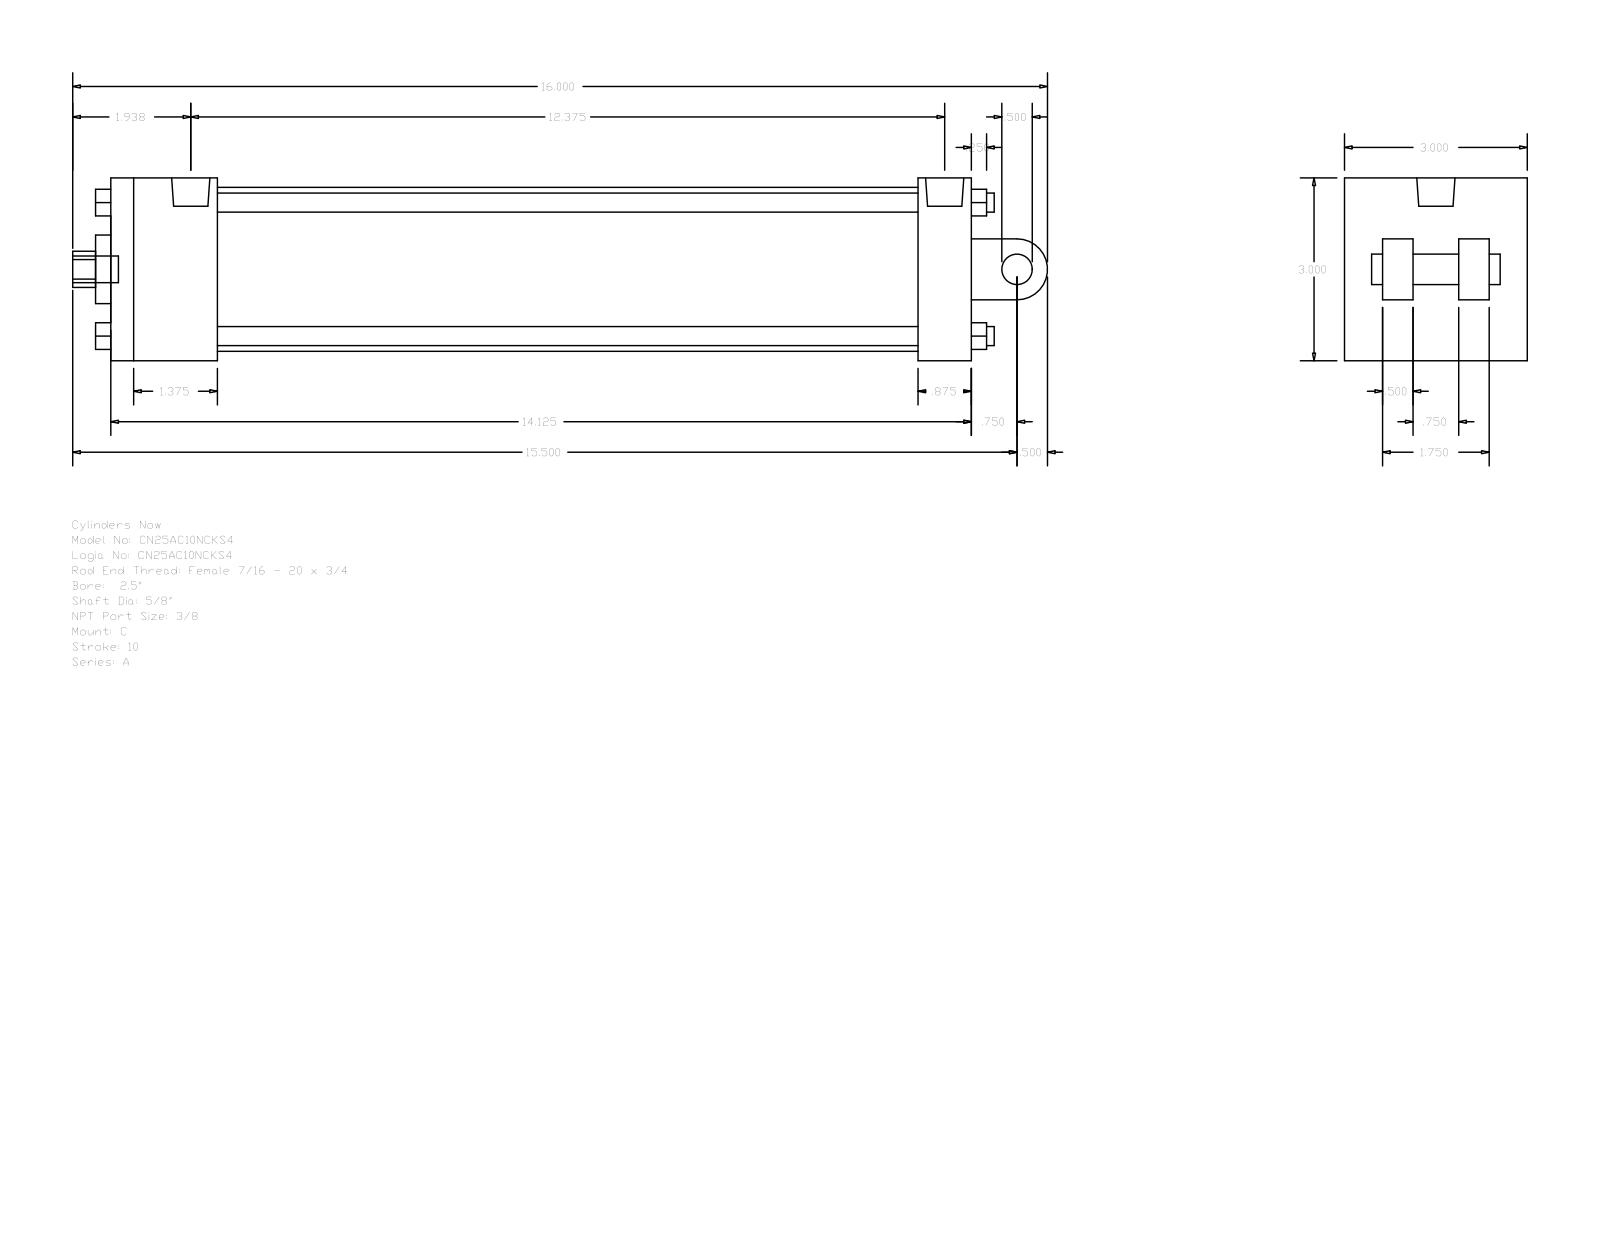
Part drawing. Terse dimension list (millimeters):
name: A_C__0250_0.625
written by: GSSL Pune (CONFIG_CONTROL_DESIGN)
unit: mm
bodies: 0 solids, 135 faces (102 planar, 33 cylindrical, 0 other)
size: 406.4 × 76.2 × 76.2
holes: 2× ⌀5.56, 1× ⌀15.88, 1× ⌀15.93, 1× ⌀28.57, 1× ⌀68.33
bosses: 4× ⌀7.94, 2× ⌀5.56, 1× ⌀15.93, 1× ⌀12.7, 1× ⌀11.11
rounds: 1× R7.54, 1× R12.7
face distances: 76.2, 358.77, 44.45, 336.55, 292.1, 314.32, 22.22, 50.8, 12.7, 15.87
hole spacings: 2.38
